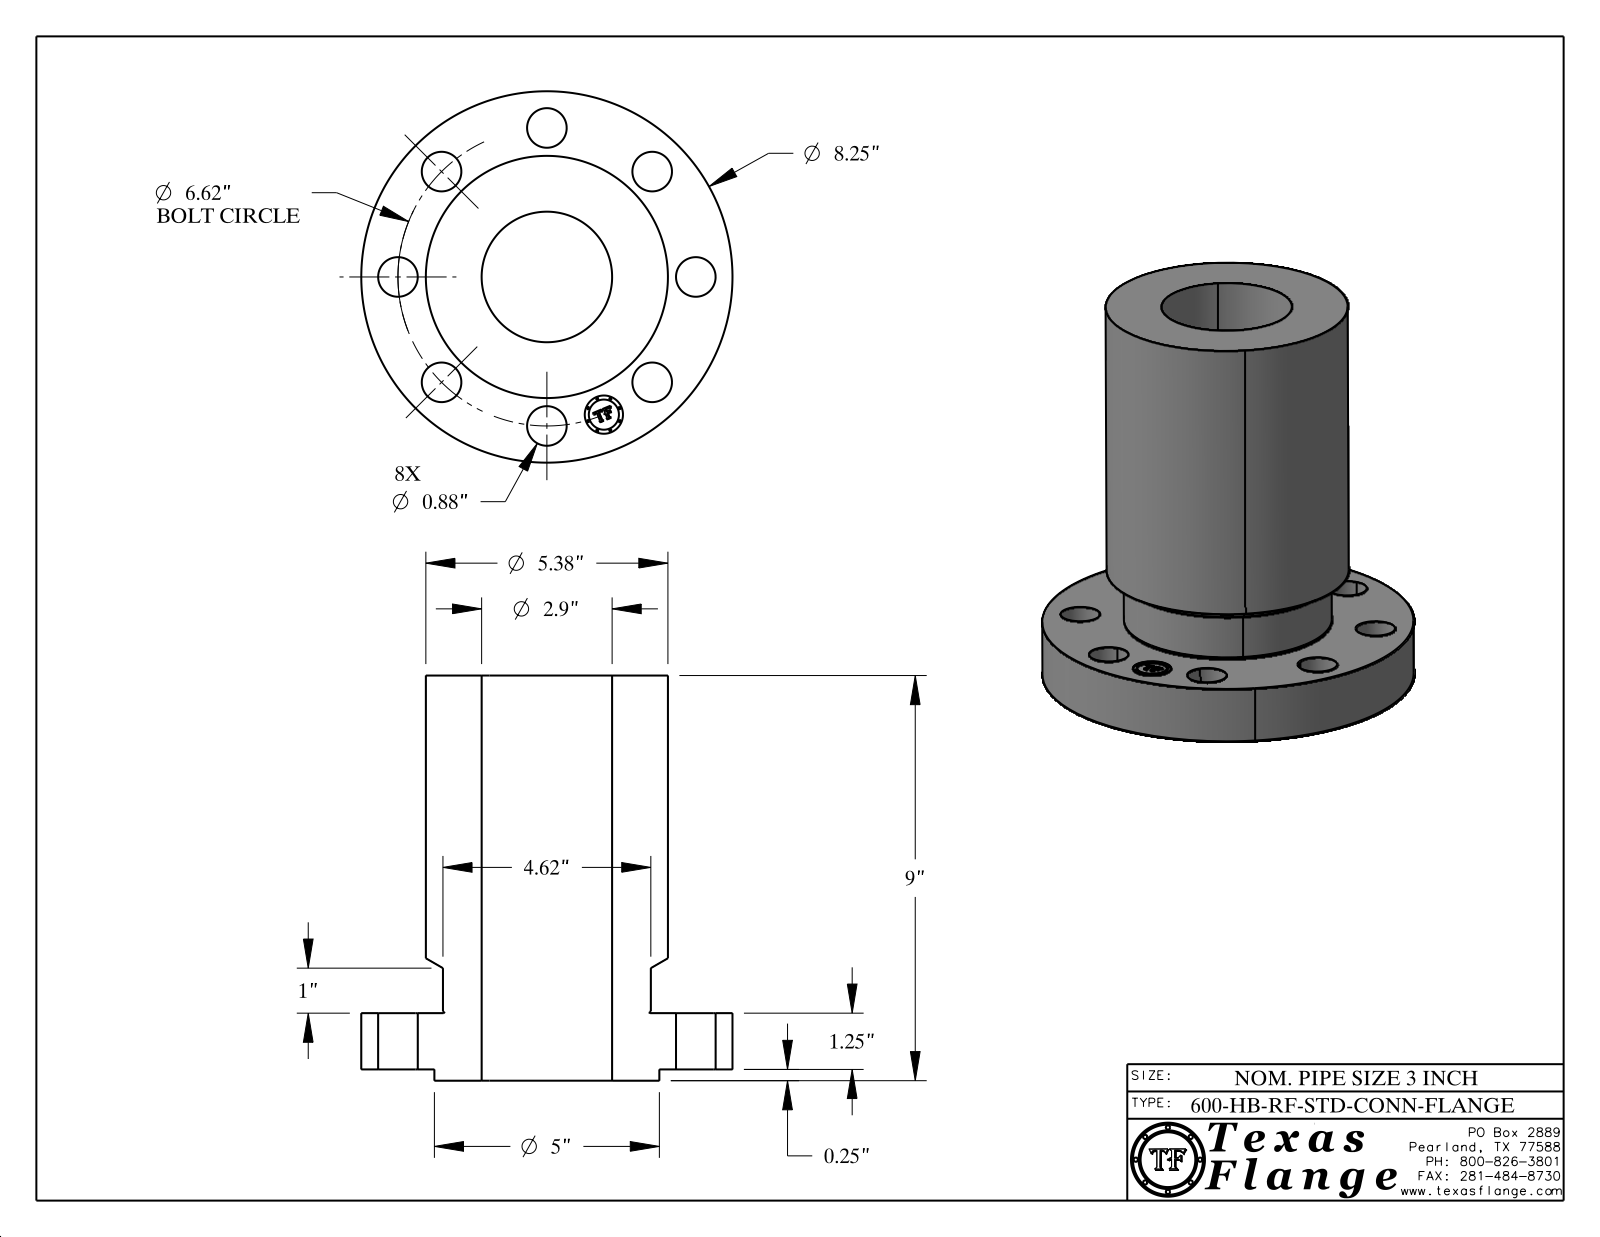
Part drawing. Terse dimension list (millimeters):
name: 3-600-HB-RF-STD-CONN-FLANGE
written by: CATIA V5 STEP AP214 (AUTOMOTIVE_DESIGN)
unit: mm
bodies: 1 solid, 421 faces (369 planar, 46 cylindrical, 6 other)
size: 228.6 × 209.6 × 209.6
volume: 2 786 000 mm³; area: 234 900 mm²
holes: 8× ⌀22.4, 1× ⌀21.6, 1× ⌀73.7
bosses: 8× ⌀1.3, 1× ⌀209.6, 1× ⌀136.7, 1× ⌀127, 1× ⌀117.3, 1× ⌀17
face distances: 31.8, 222.3, 190.5, 6.4, 38.1, 228.6, 38, 31.6, 190.6, 0.4
hole spacings: 84.1, 64.3, 155.3, 118.9, 118.9, 32.8, 93.4, 164.9
